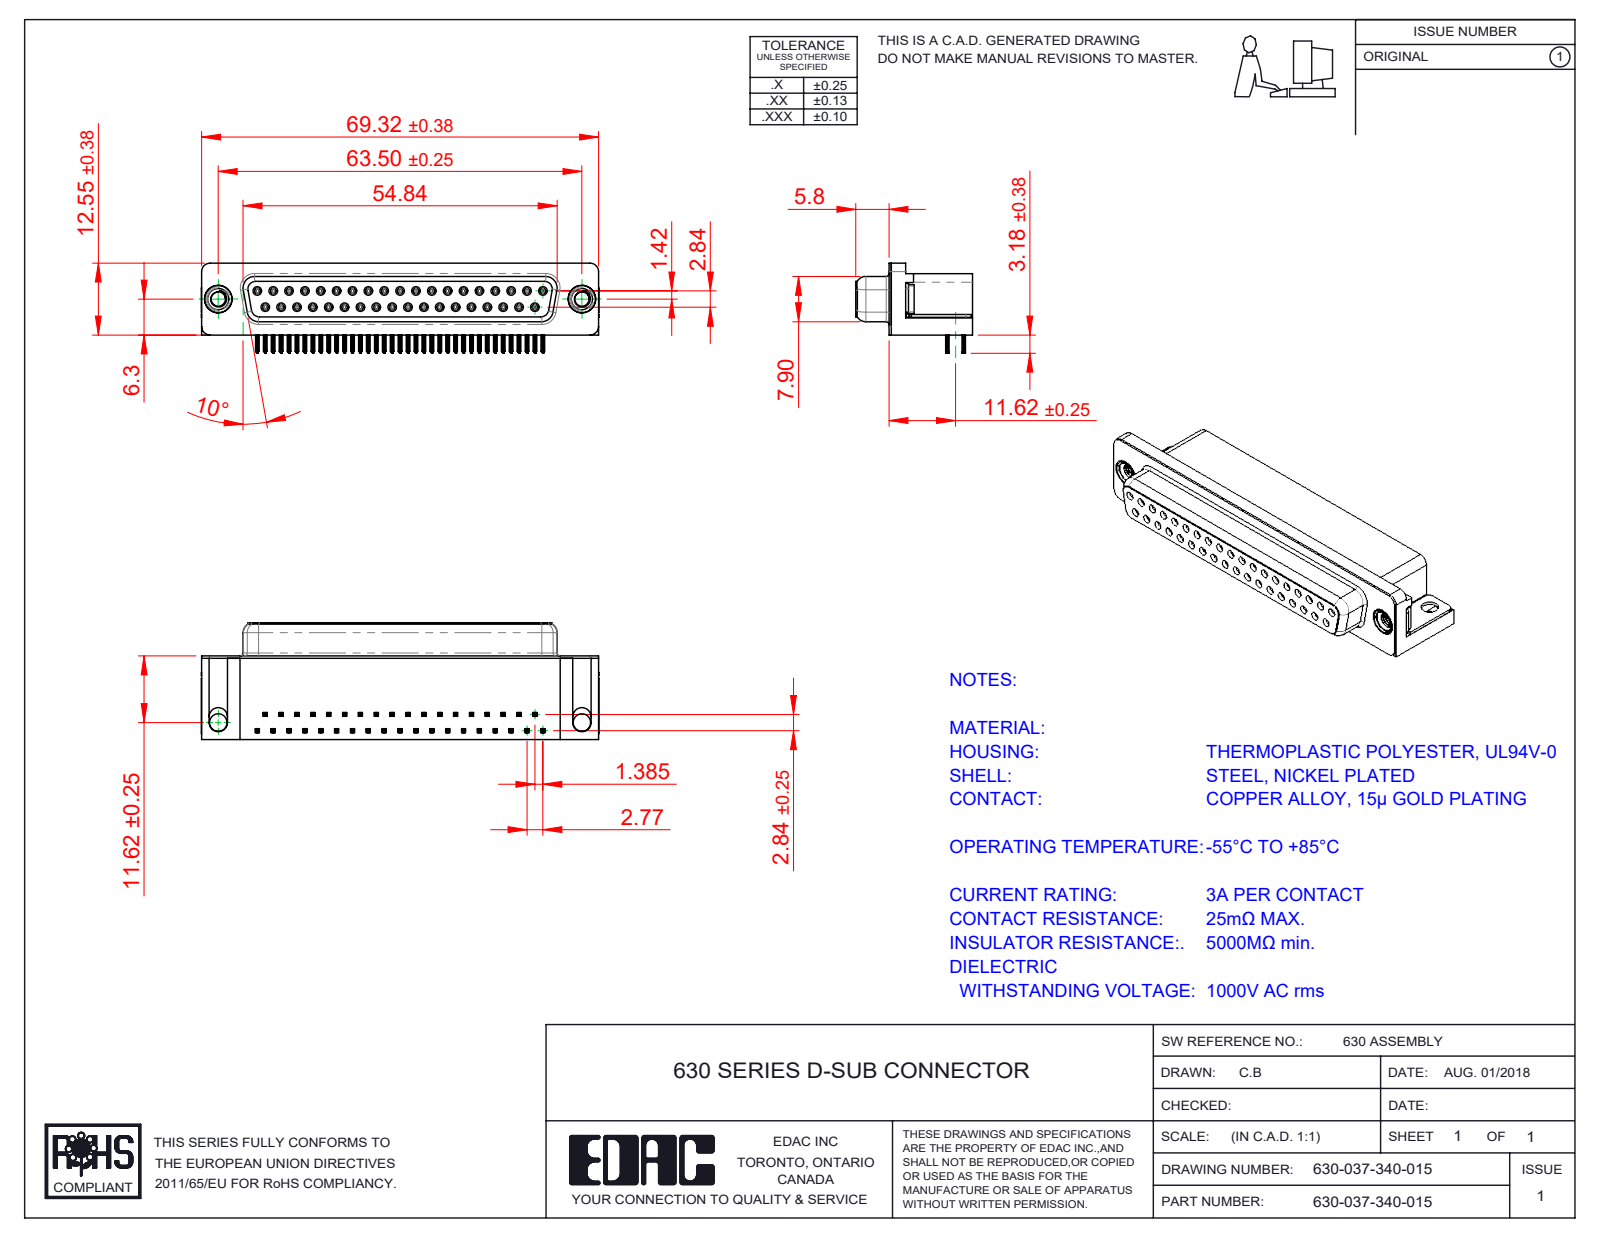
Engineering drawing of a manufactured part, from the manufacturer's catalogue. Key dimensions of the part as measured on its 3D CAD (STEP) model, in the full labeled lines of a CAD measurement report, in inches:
Part name (STEP PRODUCT): 630 M3 Threaded Rivet; 630 Contact Top; 630 Thru Hole Board Mount; 630 Shell_37 Socket (+3 more)
STEP written by: SolidWorks 2020 (CONFIG_CONTROL_DESIGN)
Units: inches
Bodies: 43 solids, 5560 faces (2502 planar, 1302 cylindrical, 1756 other)
Overall size (bounding box): 2.732 × 0.803 × 0.619
Volume: 0.721 in³ · Surface area: 20.98 in²
Round holes (diameter × count): ⌀0.031 ×37, ⌀0.035 ×37, ⌀0.098 ×2, ⌀0.12 ×2, ⌀0.157 ×2, ⌀0.189 ×2, ⌀0.197 ×2
Round bosses / shafts (diameter × count): ⌀0.047 ×37, ⌀0.193 ×2, ⌀0.187 ×2, ⌀0.154 ×2
Partial cylindrical surfaces — rounded edges, fillets, slot ends (radius × count): R0.004 ×296, R0.006 ×148, R0.014 ×74, R0.013 ×37, R0.011 ×18, R0.039 ×18, R0.01 ×8, R0.053 ×8
Main face-to-face distances: 0.016, 0.407, 0.244, 0.559, 0.262, 0.033, 0.112, 0.018, 0.575, 0.114
Hole centre spacings: 0.124, 0.109, 0.218, 0.327, 0.436, 0.545, 0.654, 0.763
